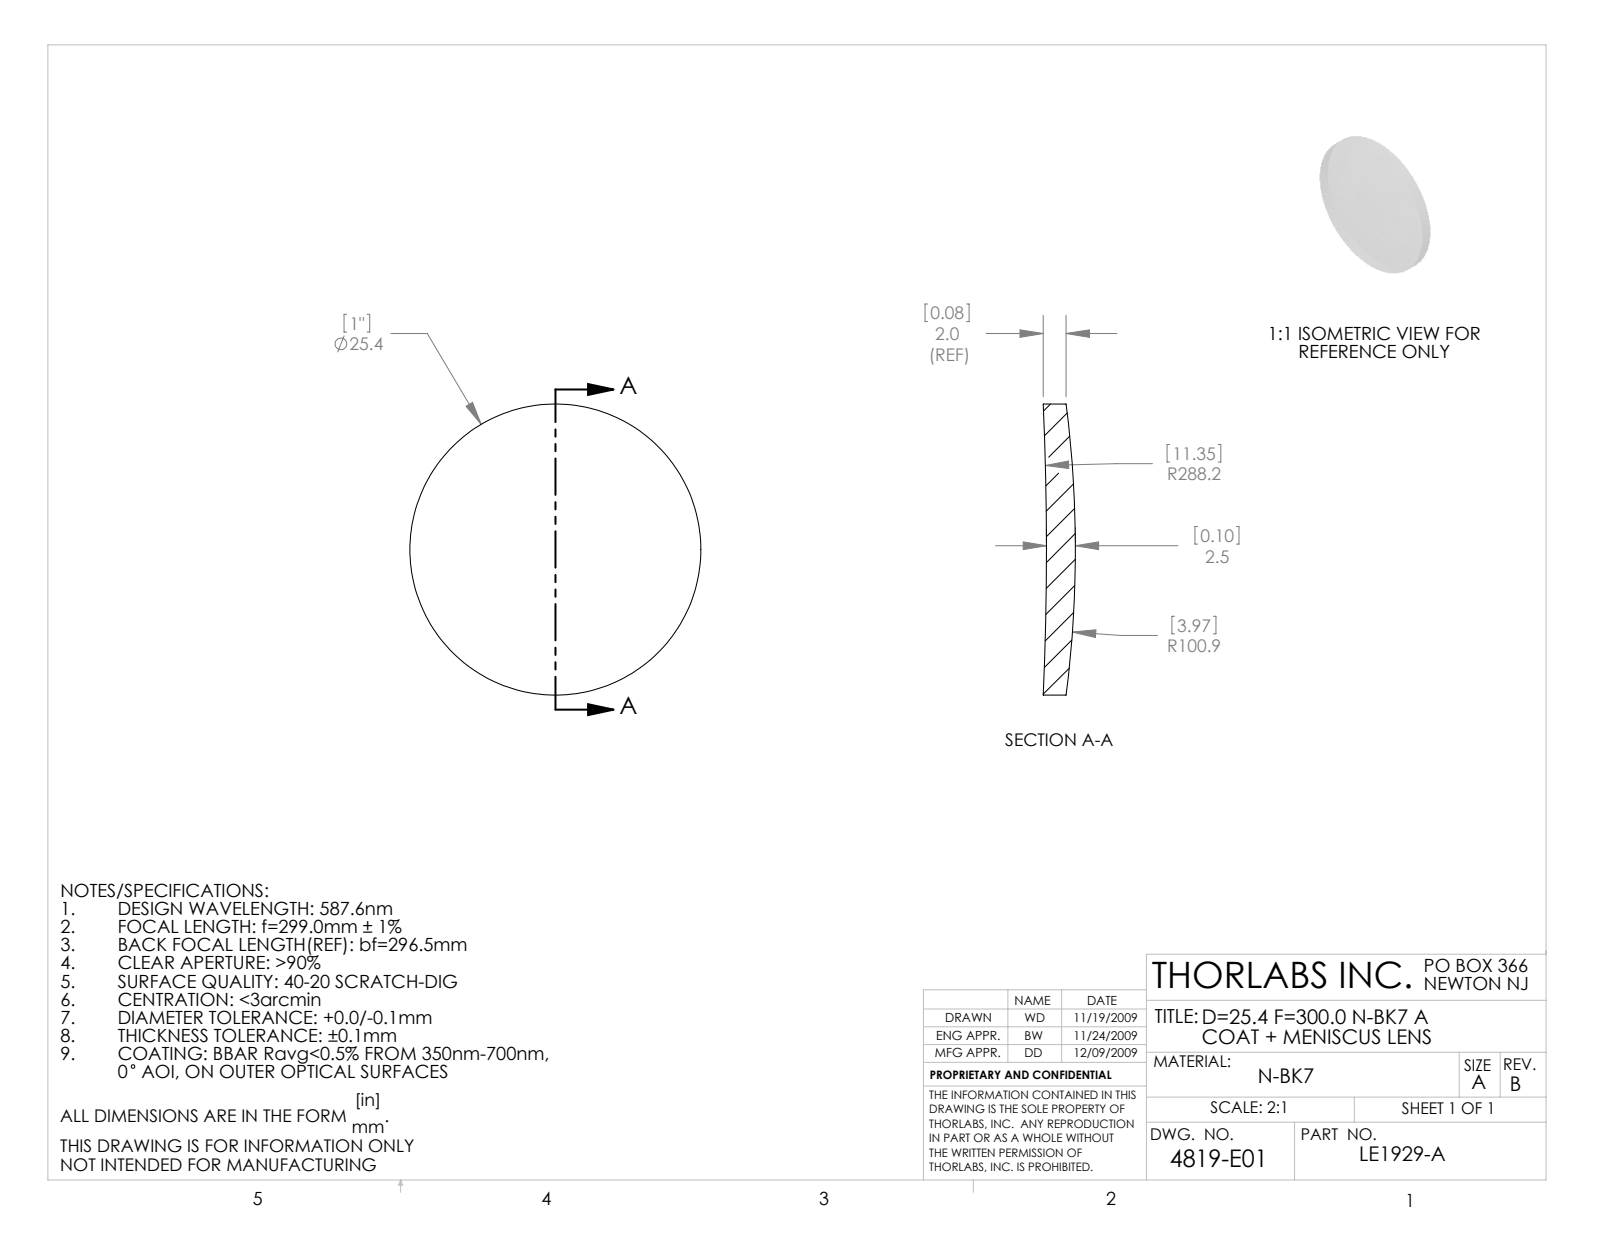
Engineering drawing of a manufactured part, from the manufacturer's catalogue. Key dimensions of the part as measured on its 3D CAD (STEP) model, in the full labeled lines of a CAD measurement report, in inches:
Part name (STEP PRODUCT): 4819-E0W
STEP written by: SolidWorks 2009 (AUTOMOTIVE_DESIGN)
Units: inches
Bodies: 1 solid, 6 faces (0 planar, 2 cylindrical, 4 other)
Overall size (bounding box): 1 × 1 × 0.11
Volume: 0.07 in³ · Surface area: 1.821 in²
Round bosses / shafts (diameter × count): ⌀1 ×1
